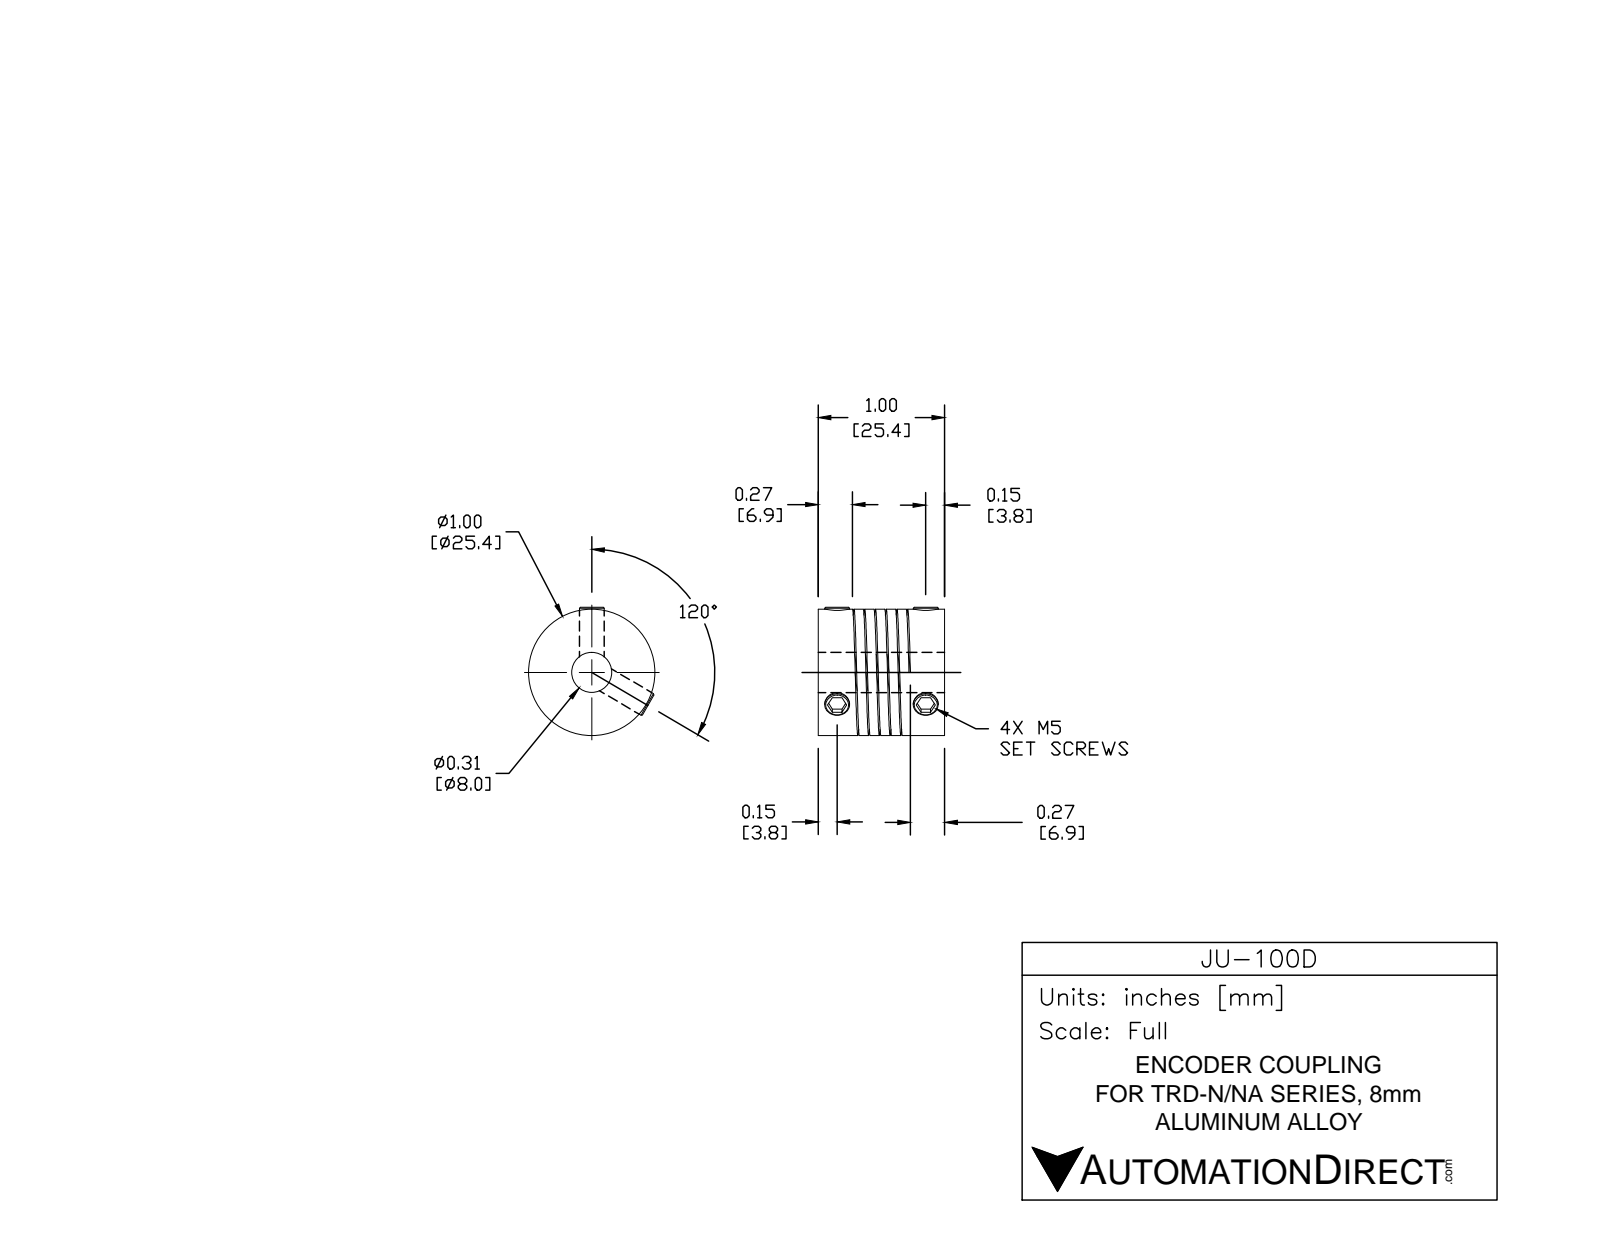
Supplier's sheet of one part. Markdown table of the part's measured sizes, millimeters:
| quantity | value |
| --- | --- |
| part name | JU-100D |
| STEP written by | SolidWorks 2016 (AUTOMOTIVE_DESIGN) |
| units | millimeters |
| bodies | 1 solid, 142 faces (58 planar, 46 cylindrical, 38 other) |
| overall size | 25.4 × 25.4 × 25.4 |
| volume | 9 670 mm³ |
| surface area | 7 006 mm² |
| round holes (diameter × count) | 2.5 × 4, 5 × 4, 8 × 1, 12 × 1 |
| round bosses / shafts (diameter × count) | 25.4 × 1 |
| main face-to-face distances | 25.4, 6.6, 18.8, 12.2, 15.46, 15.36, 1.5 |
| hole center spacings | 17.8 |
